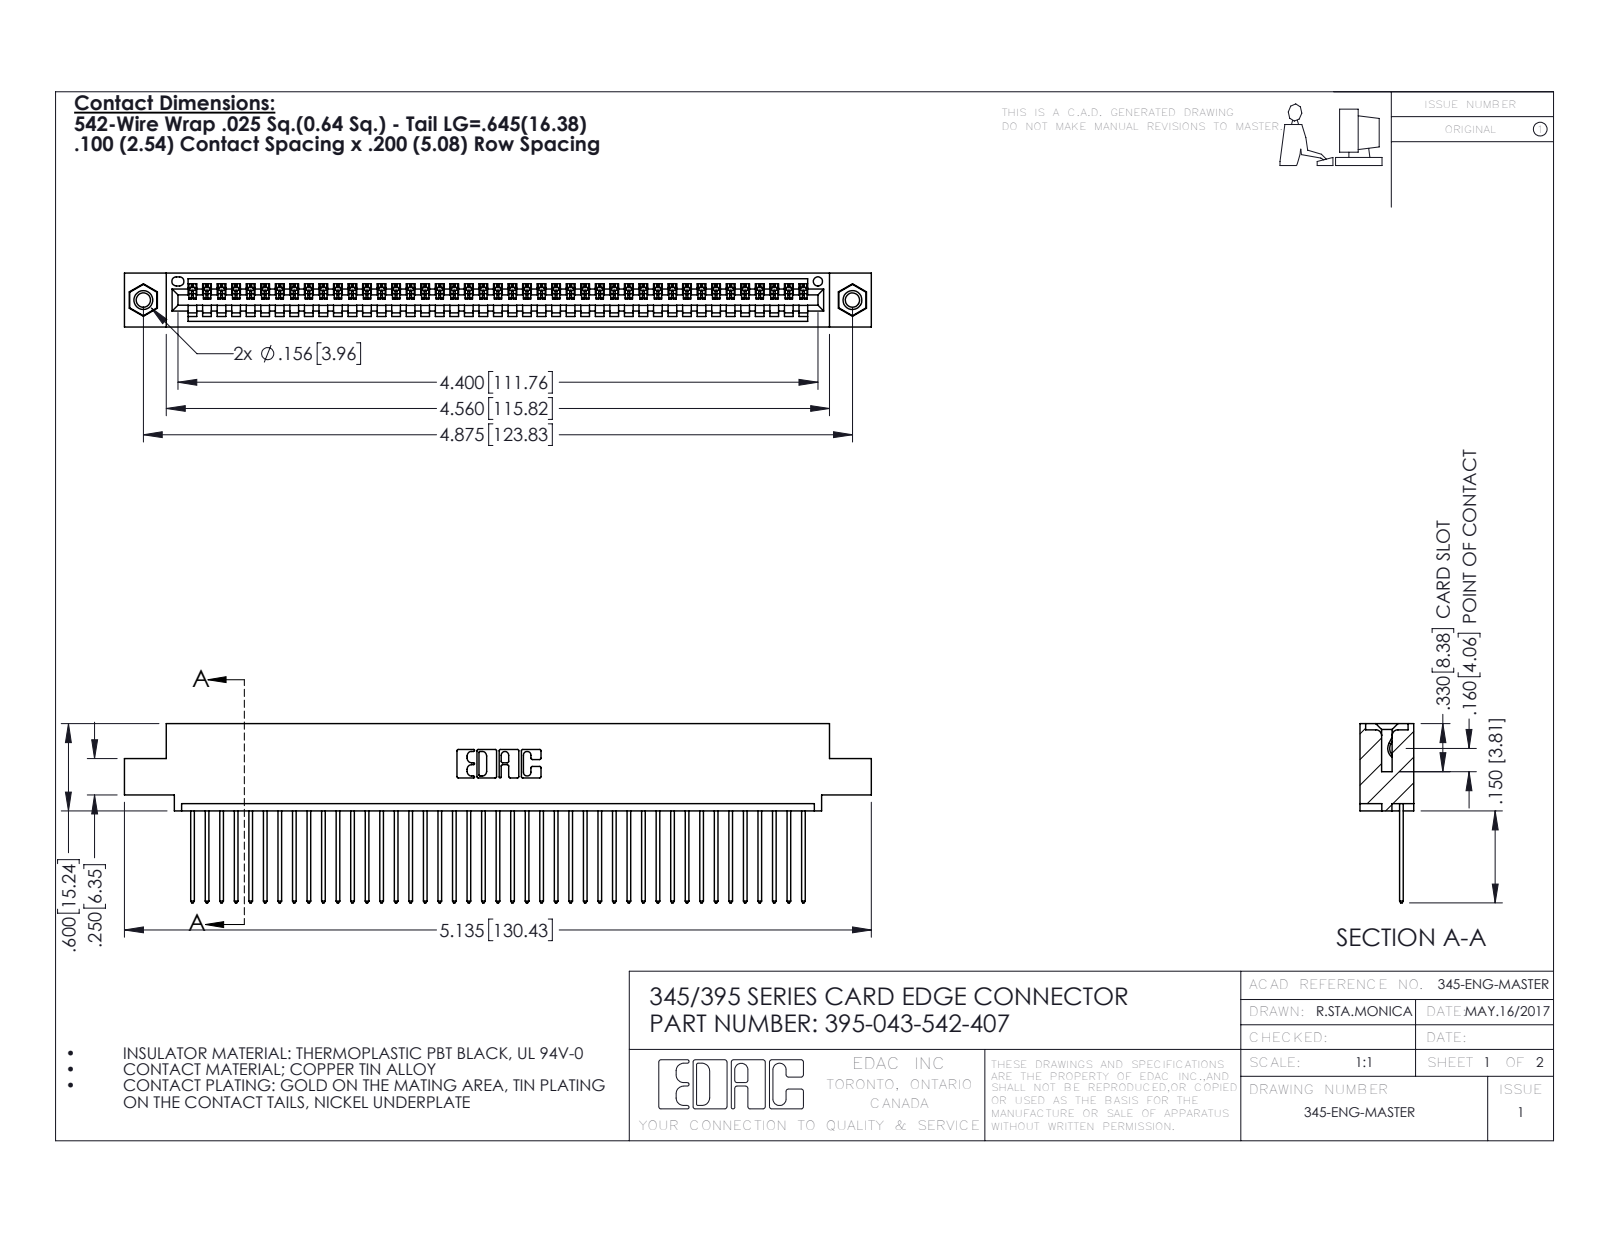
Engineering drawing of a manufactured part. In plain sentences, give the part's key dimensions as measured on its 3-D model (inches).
The part is named "345-292-001_345-293-142; 345-250-001_345-250-005-103; 395-043-542-407; 345 Part_0.110 Offset - 0.156 Dia-TI". Its 3-D file was written by "SolidWorks 2016 (CONFIG_CONTROL_DESIGN)". It is 46 solids with 2684 faces: 1836 planar, 832 cylindrical and 16 other. Overall it measures 5.135 by 1.232 by 0.37 inches. Its volume is 0.757 cubic inches and its surface area 26.69 square inches. Round holes: 2 of diameter 0.098, 2 of diameter 0.125, 2 of diameter 0.156, 1 of diameter 0.064. Round bosses or shafts: 2 of diameter 0.155. Partial cylindrical surfaces (rounded edges, fillets, slot ends): 86 of radius 0.006, 86 of radius 0.01, 22 of radius 0.01, 6 of radius 0.007, 6 of radius 0.031, 3 of radius 0.026, 2 of radius 0.031, 2 of radius 0.04. The main face-to-face distances are 0.072, 0.298, 0.37, 0.098, 0.272, 0.025, 0.2, 0.225, 0.149, 0.072. The hole center spacings are 0.27, 4.639, 4.875.
